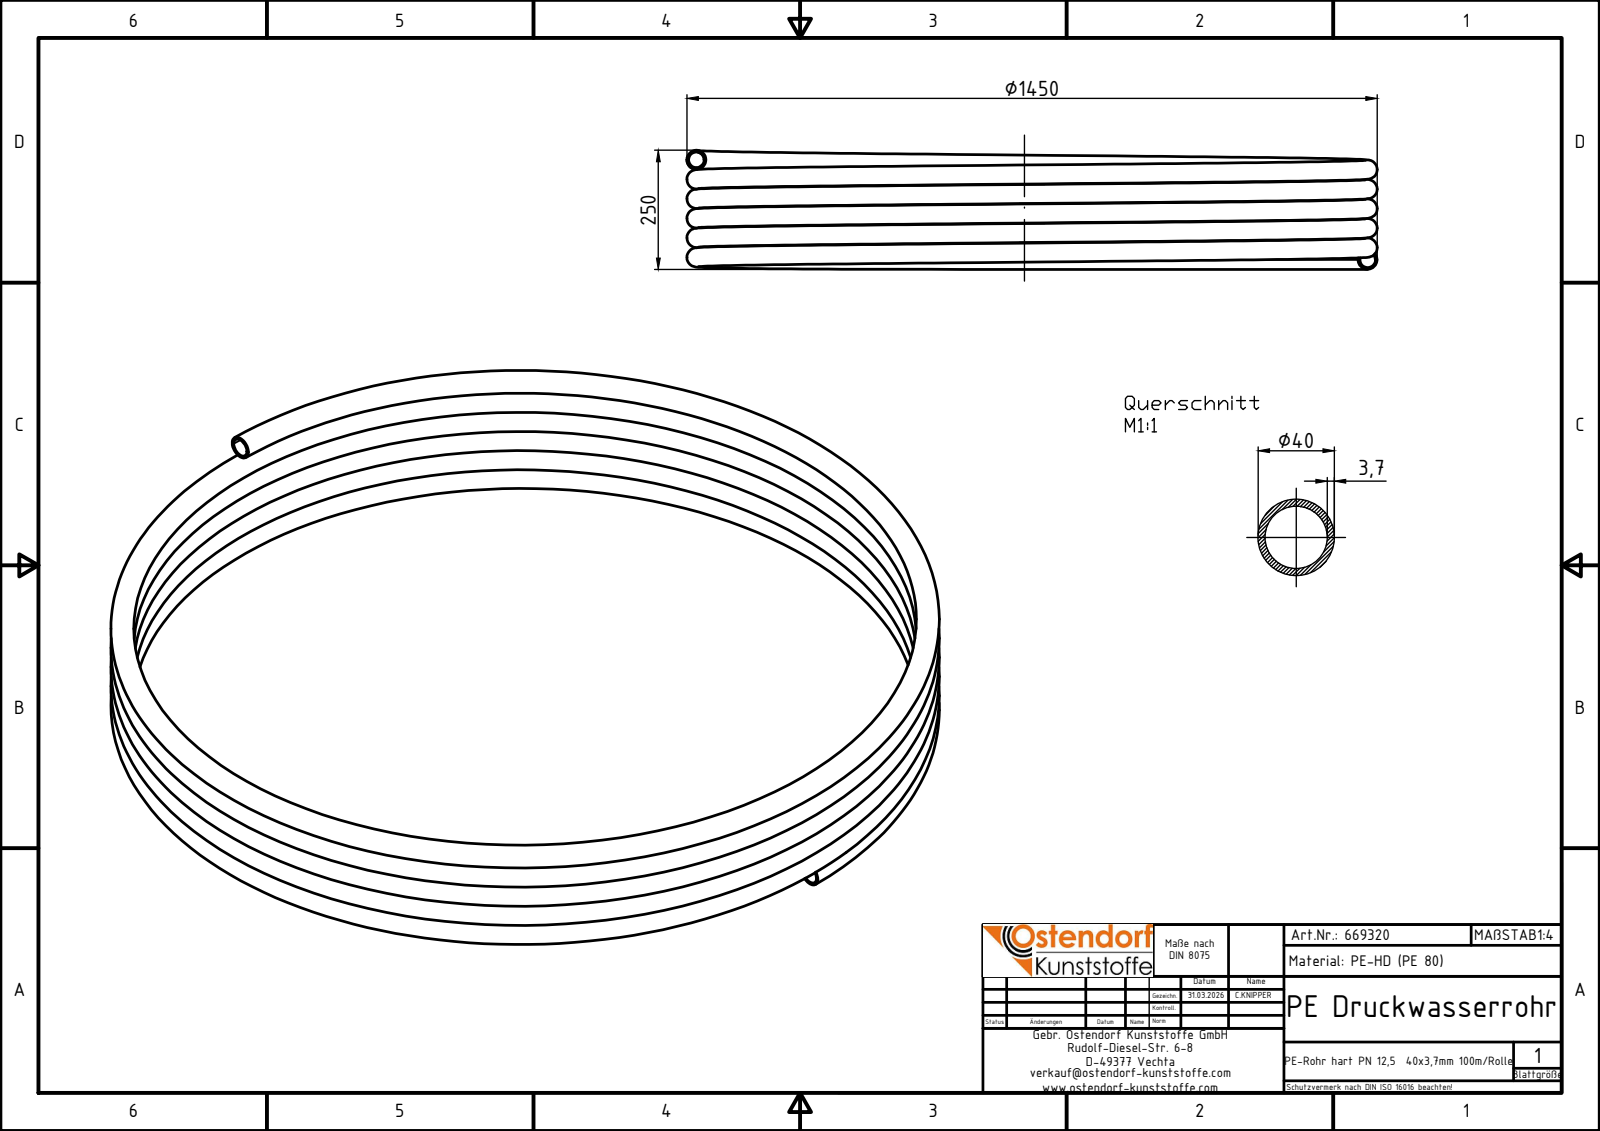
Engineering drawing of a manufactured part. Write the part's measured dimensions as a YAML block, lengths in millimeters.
part_name: "669320z"
step_written_by: "Autodesk Inventor 2024 (AUTOMOTIVE_DESIGN)"
units: millimeters
bodies: {solids: 1, faces: 7, planar: 3, cylindrical: 0, other: 4}
overall_size: [1450.01, 1450.01, 250.12]
volume: 10090000
surface_area: 5463000
